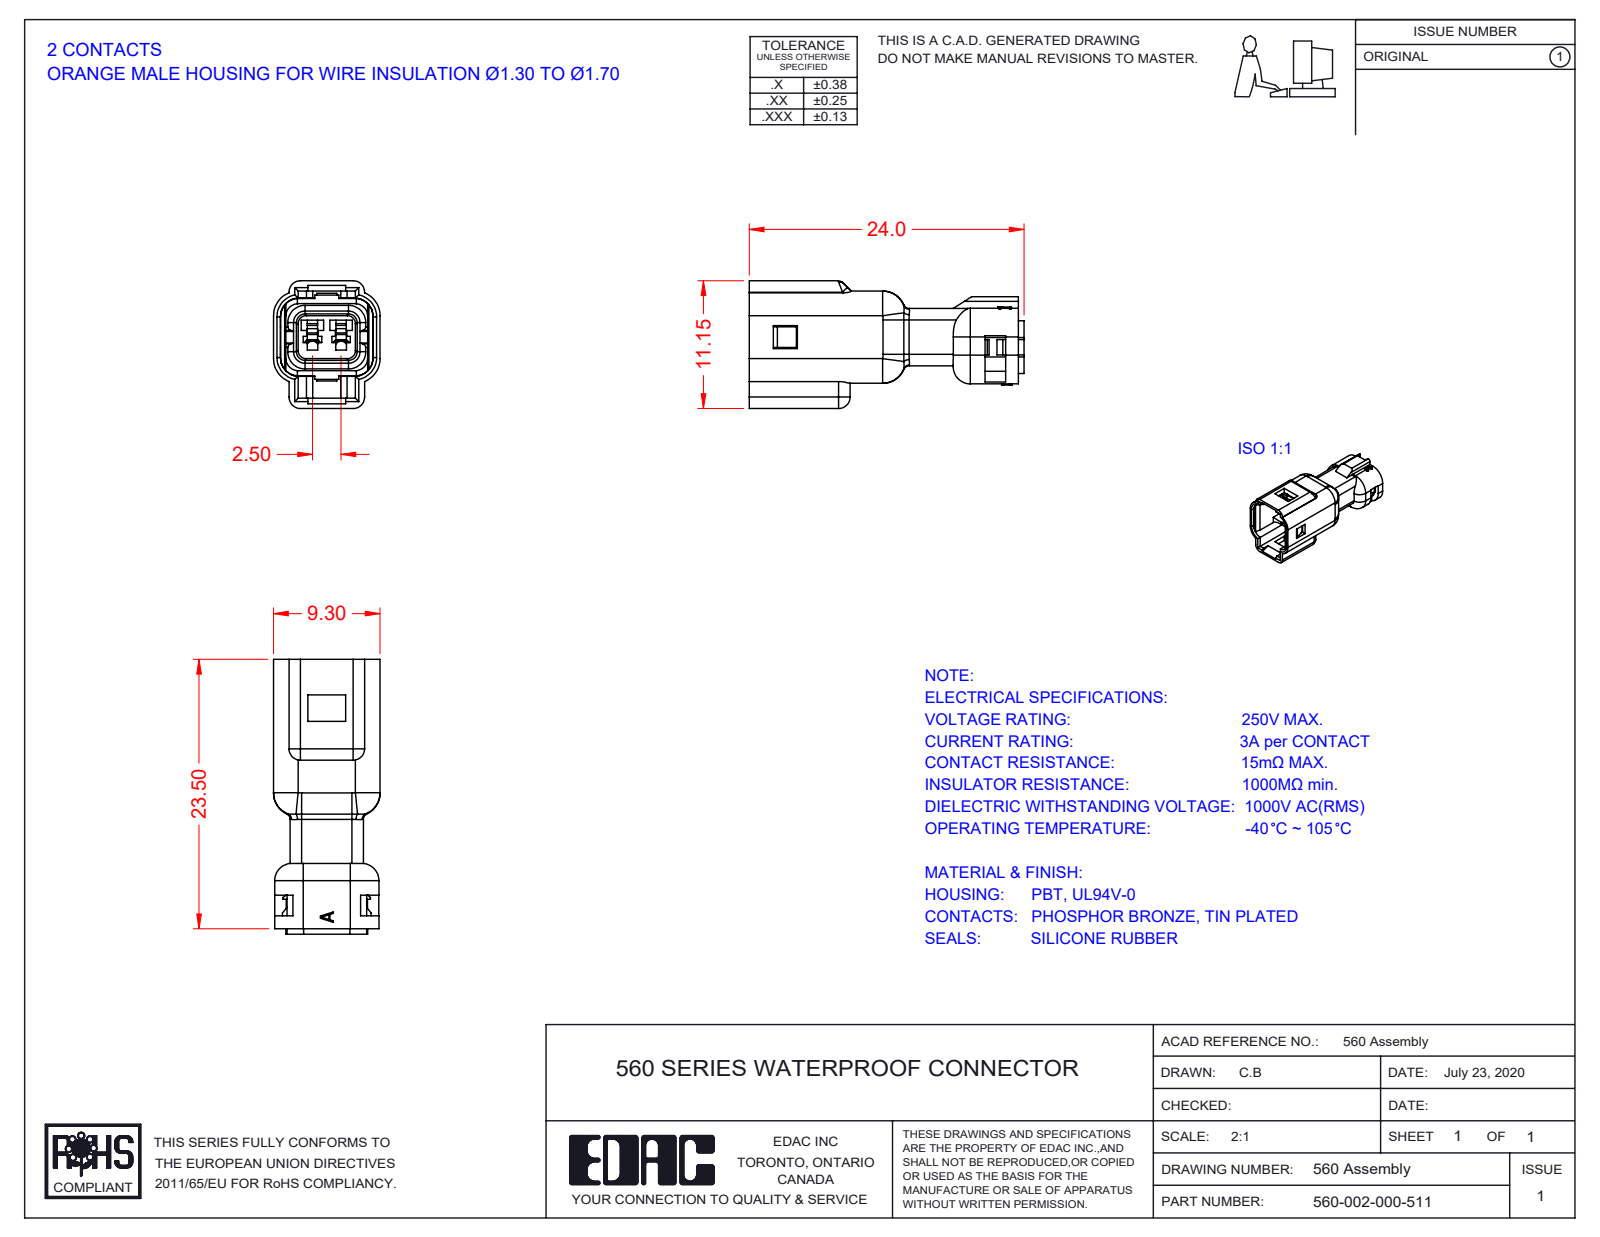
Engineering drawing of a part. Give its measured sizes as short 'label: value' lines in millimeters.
name: REAR-GASKET-2POS_ORANGE; INTERNAL-WIRE-SEAL-2POS; MALE-HOUSING-2POS_ORANGE; 560-002-000-511 (+2 more)
written by: SolidWorks 2020 (CONFIG_CONTROL_DESIGN)
unit: mm
bodies: 5 solids, 895 faces (495 planar, 209 cylindrical, 191 other)
size: 23.98 × 11.15 × 9.3
volume: 900 mm³; area: 2 421 mm²
holes: 2× ⌀1.5
rounds: 25× R1, 16× R0.25, 13× R0.35, 12× R1.2, 9× R0.15, 8× R1.5, 8× R1.65, 5× R0.5
face distances: 0.6, 0.9, 1.07, 8.7, 7.6, 8.1, 2.15, 7.15, 0.8, 4.7
hole spacings: 2.5
